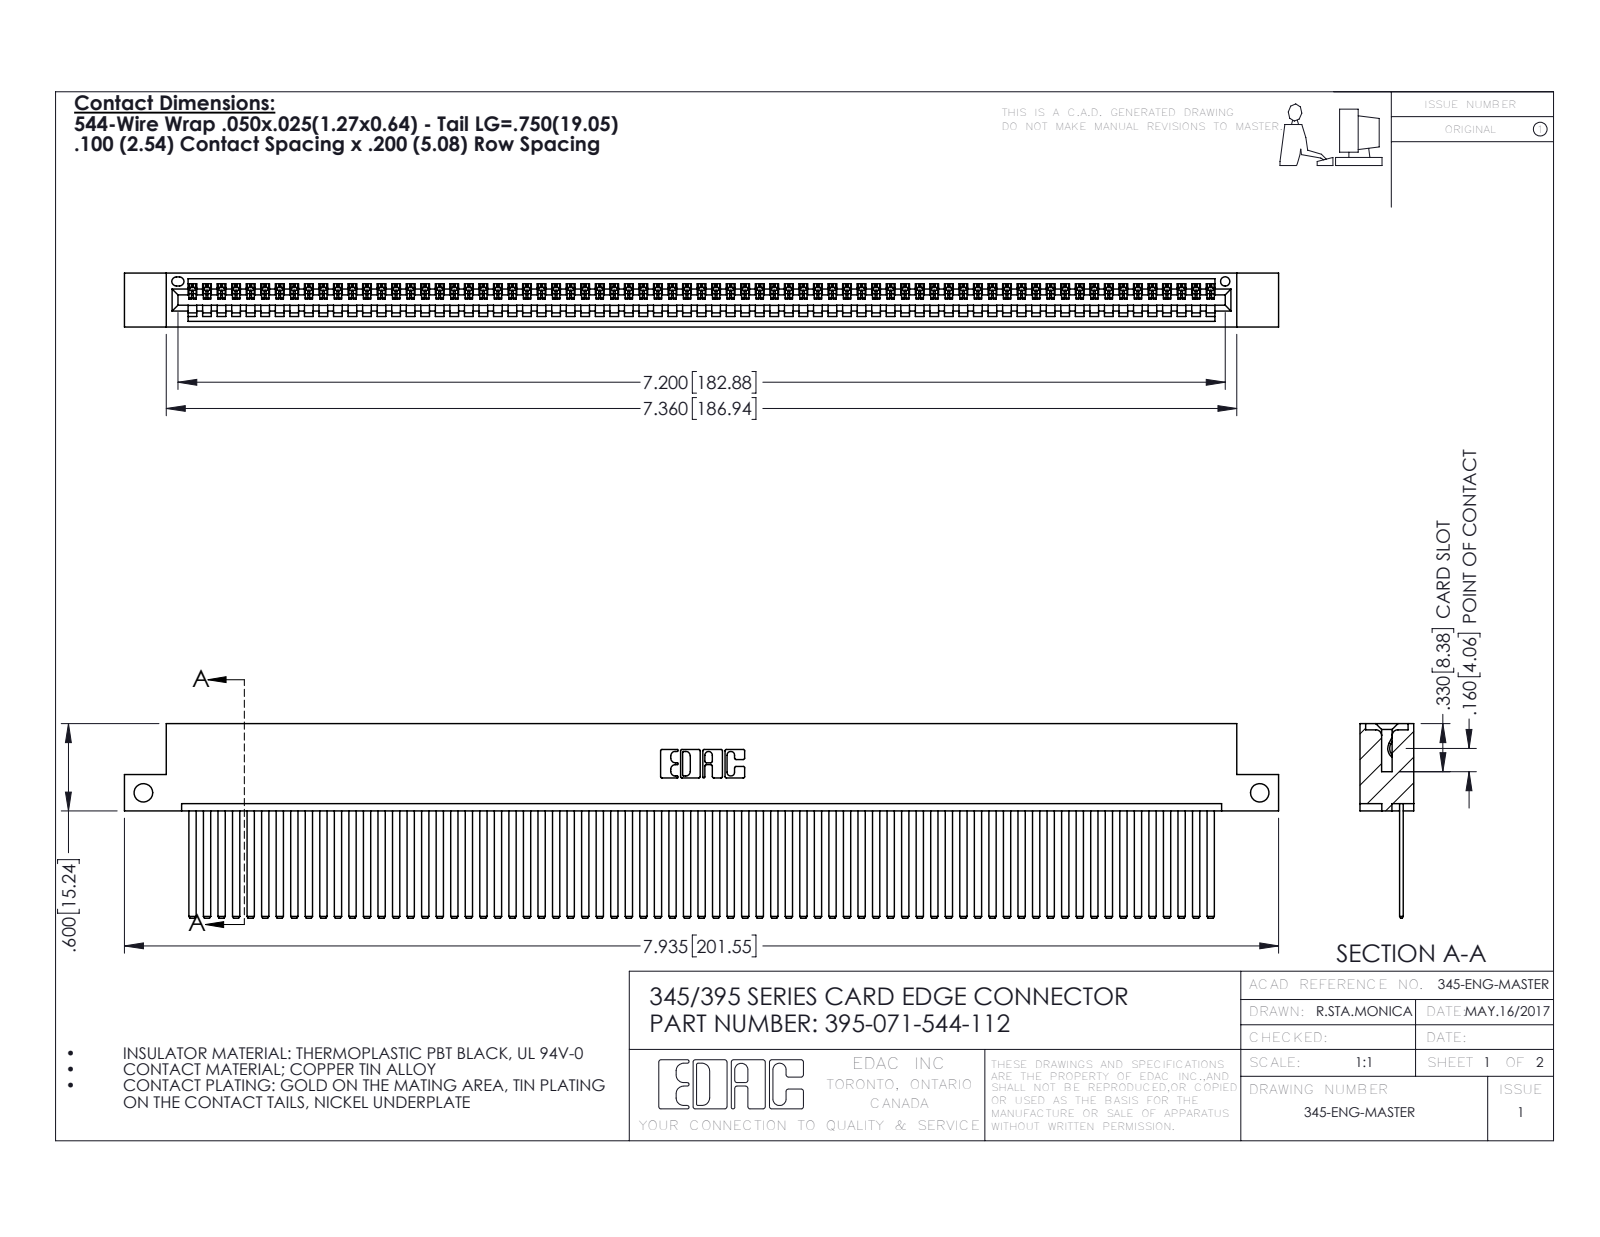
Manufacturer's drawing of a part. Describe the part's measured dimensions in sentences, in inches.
The part is named "345-292-001_345-293-144; 345 Part_Flush Mounting Lugs - Side Mount; 395-071-544-112". Its 3-D file was written by "SolidWorks 2016 (CONFIG_CONTROL_DESIGN)". It is 72 solids with 3818 faces: 2636 planar, 1182 cylindrical and 0 other. Overall it measures 7.935 by 1.337 by 0.37 inches. Its volume is 1.228 cubic inches and its surface area 45.65 square inches. Round holes: 2 of diameter 0.128, 1 of diameter 0.064. Partial cylindrical surfaces (rounded edges, fillets, slot ends): 142 of radius 0.006, 22 of radius 0.01, 6 of radius 0.007, 6 of radius 0.031, 3 of radius 0.026, 2 of radius 0.031, 2 of radius 0.04, 1 of radius 0.014. The main face-to-face distances are 0.072, 0.298, 0.025, 0.098, 0.272, 0.37, 0.2, 0.225, 0.149, 0.072. The hole center spacings are 7.675.
